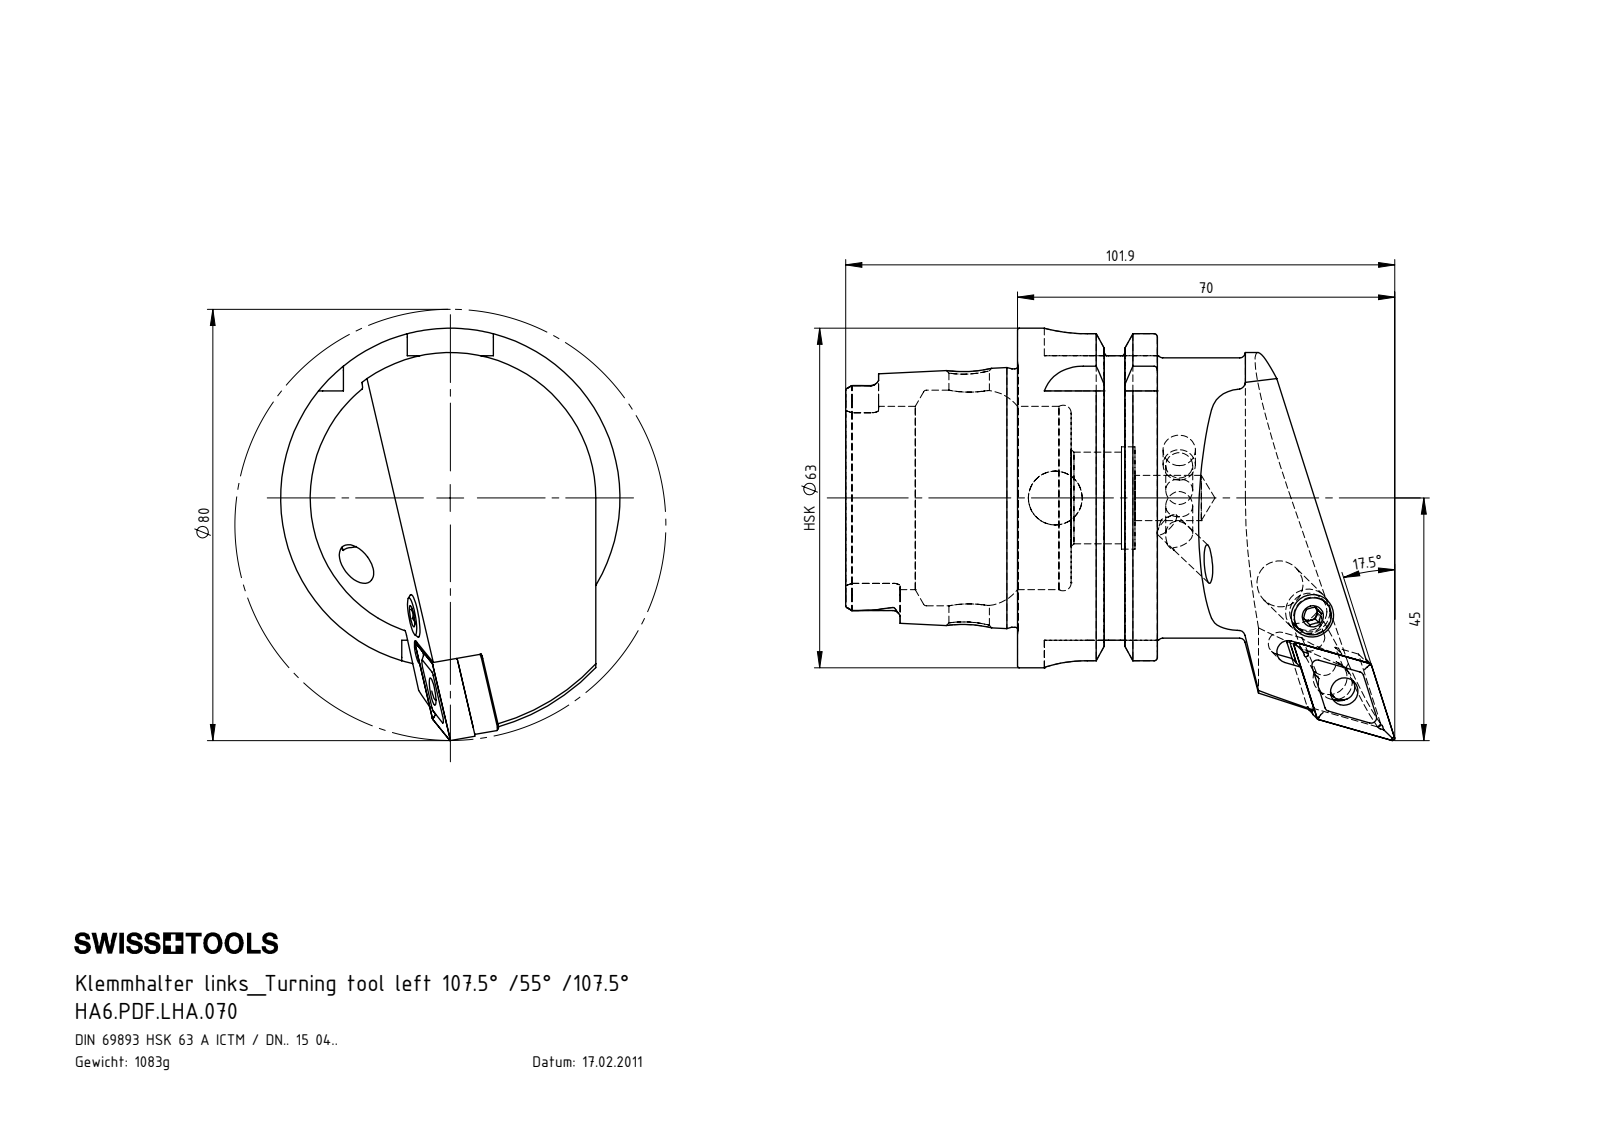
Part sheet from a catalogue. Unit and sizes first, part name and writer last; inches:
Units: inches
Overall size (bounding box): 4.012 × 3.012 × 2.48
Round holes (diameter × count): ⌀0.197 ×3, ⌀0.331 ×2, ⌀0.203 ×1, ⌀0.236 ×1, ⌀0.252 ×1, ⌀0.276 ×1, ⌀0.295 ×1, ⌀0.394 ×1, ⌀0.669 ×1, ⌀0.748 ×1, ⌀1.339 ×1, ⌀1.575 ×1
Round bosses / shafts (diameter × count): ⌀2.48 ×1, ⌀2.163 ×1, ⌀2.047 ×1, ⌀1.887 ×1, ⌀0.315 ×1, ⌀0.311 ×1, ⌀0.252 ×1, ⌀0.236 ×1
Partial cylindrical surfaces — rounded edges, fillets, slot ends (radius × count): R0.055 ×6, R0.016 ×4, R0.039 ×4, R0.113 ×4, R0.315 ×4, R0.098 ×2, R0.083 ×1, R0.093 ×1
Main face-to-face distances: 1.022, 0.63, 0.392, 1.256, 1.648, 2.278, 0.238, 2.079, 0.858, 0.125
Hole centre spacings: 0.614
Volume: 8.381 in³ · Surface area: 51.04 in²
Bodies: 7 solids, 356 faces (109 planar, 100 cylindrical, 147 other)
Part name (STEP PRODUCT): HA6-PDF.LHA.070; KVT_MB_600_060; WCD-ER4.101.017_A; WDF-ER3.101.000_A (+3 more)
STEP written by: SolidWorks 2012 (CONFIG_CONTROL_DESIGN)
